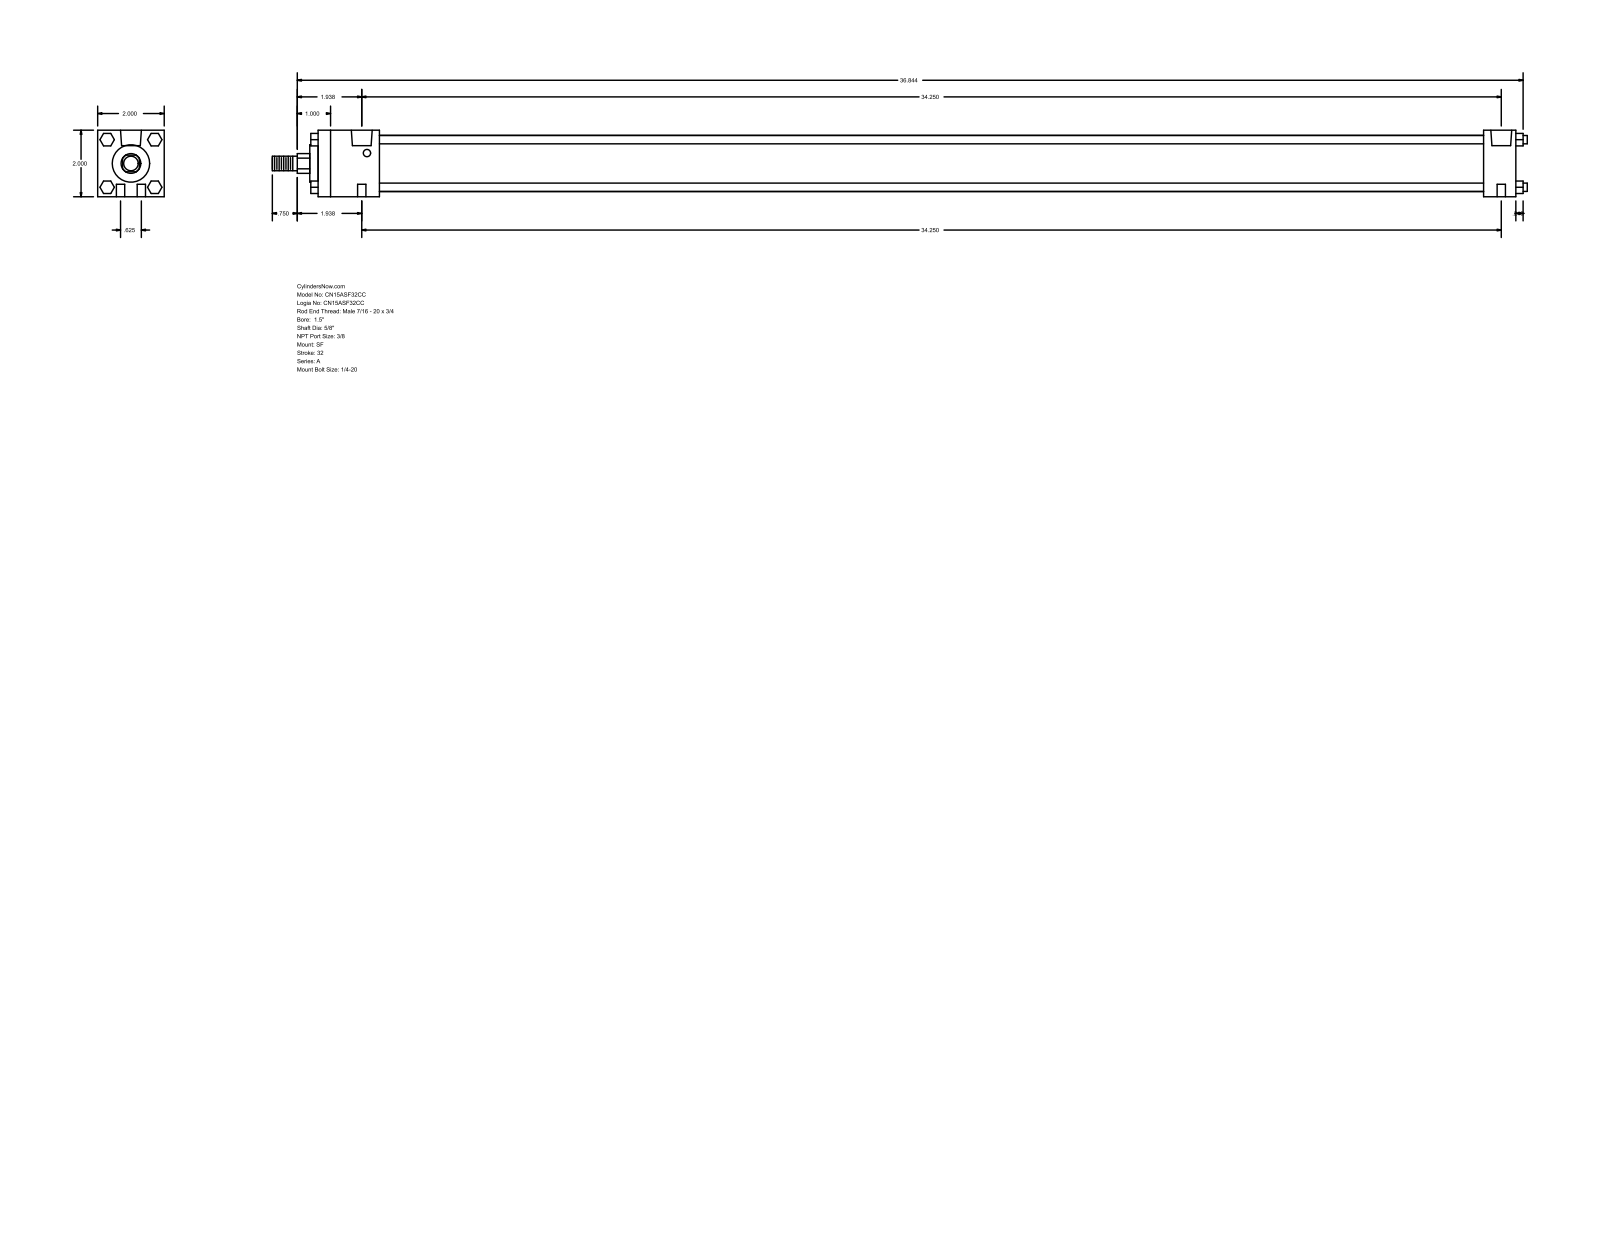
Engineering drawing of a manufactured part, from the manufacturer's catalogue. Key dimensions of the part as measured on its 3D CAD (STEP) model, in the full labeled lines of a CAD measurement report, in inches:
Part name (STEP PRODUCT): A_SF__0150_0.625
STEP written by: GSSL Pune (CONFIG_CONTROL_DESIGN)
Units: inches
Bodies: 0 solids, 124 faces (94 planar, 30 cylindrical, 0 other)
Overall size (bounding box): 37.719 × 2 × 2
Round holes (diameter × count): ⌀0.25 ×4, ⌀0.219 ×2, ⌀0.627 ×2
Round bosses / shafts (diameter × count): ⌀0.25 ×4, ⌀1.69 ×1, ⌀1.125 ×1, ⌀0.625 ×1, ⌀0.437 ×1
Partial cylindrical surfaces — rounded edges, fillets, slot ends (radius × count): R0.297 ×1
Main face-to-face distances: 2, 36, 1.844, 35.031, 33.187, 34.156, 0.969, 0.25, 0.375, 2.094
Hole centre spacings: 0.313, 34.252, 34.25, 0.625, 34.256, 33.937
